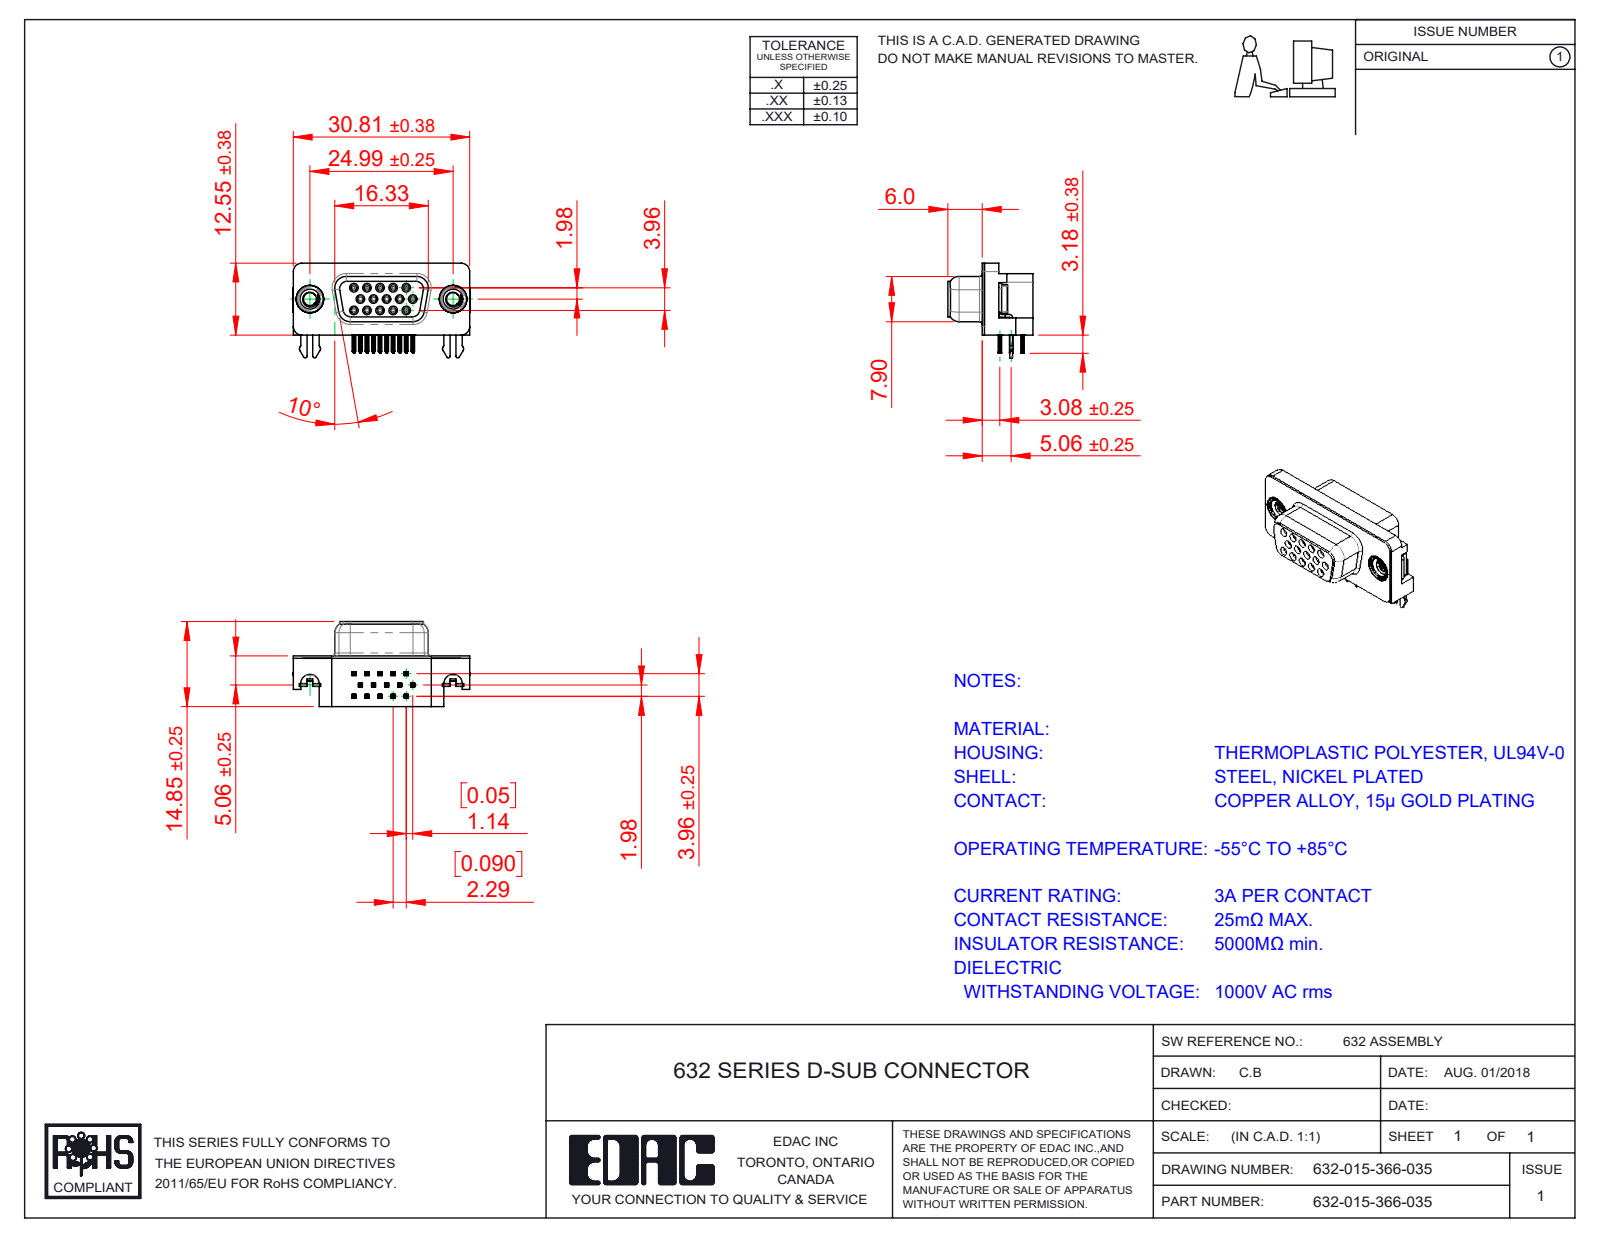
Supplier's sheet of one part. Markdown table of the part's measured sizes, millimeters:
| quantity | value |
| --- | --- |
| part name | 632 Contact Top; 632 Contact Bottom; 632 M3 Threaded Rivet; 632 Housing_15 Socket (+5 more) |
| STEP written by | SolidWorks 2016 (CONFIG_CONTROL_DESIGN) |
| units | millimeters |
| bodies | 23 solids, 2426 faces (1006 planar, 654 cylindrical, 766 other) |
| overall size | 30.89 × 16.55 × 14.85 |
| volume | 2 996 mm³ |
| surface area | 5 342 mm² |
| round holes (diameter × count) | 0.8 × 15, 0.9 × 15, 2.26 × 2, 2.5 × 2, 4 × 2, 4.8 × 2, 5 × 2 |
| round bosses / shafts (diameter × count) | 1.2 × 15, 4.9 × 2, 4.75 × 2, 3.9 × 2 |
| partial cylindrical surfaces (radius × count) | 0.1 × 120, 0.15 × 60, 0.35 × 30, 0.34 × 15, 1 × 11, 0.28 × 10, 0.5 × 10, 0.25 × 8 |
| main face-to-face distances | 0.4, 8.45, 8.85, 1.98, 2.9, 5.95, 2.5, 6.4, 6.7, 7.05 |
| hole center spacings | 2.28, 2.29, 3.96, 4.57, 6.05, 3.97, 4.58, 6.86 |
